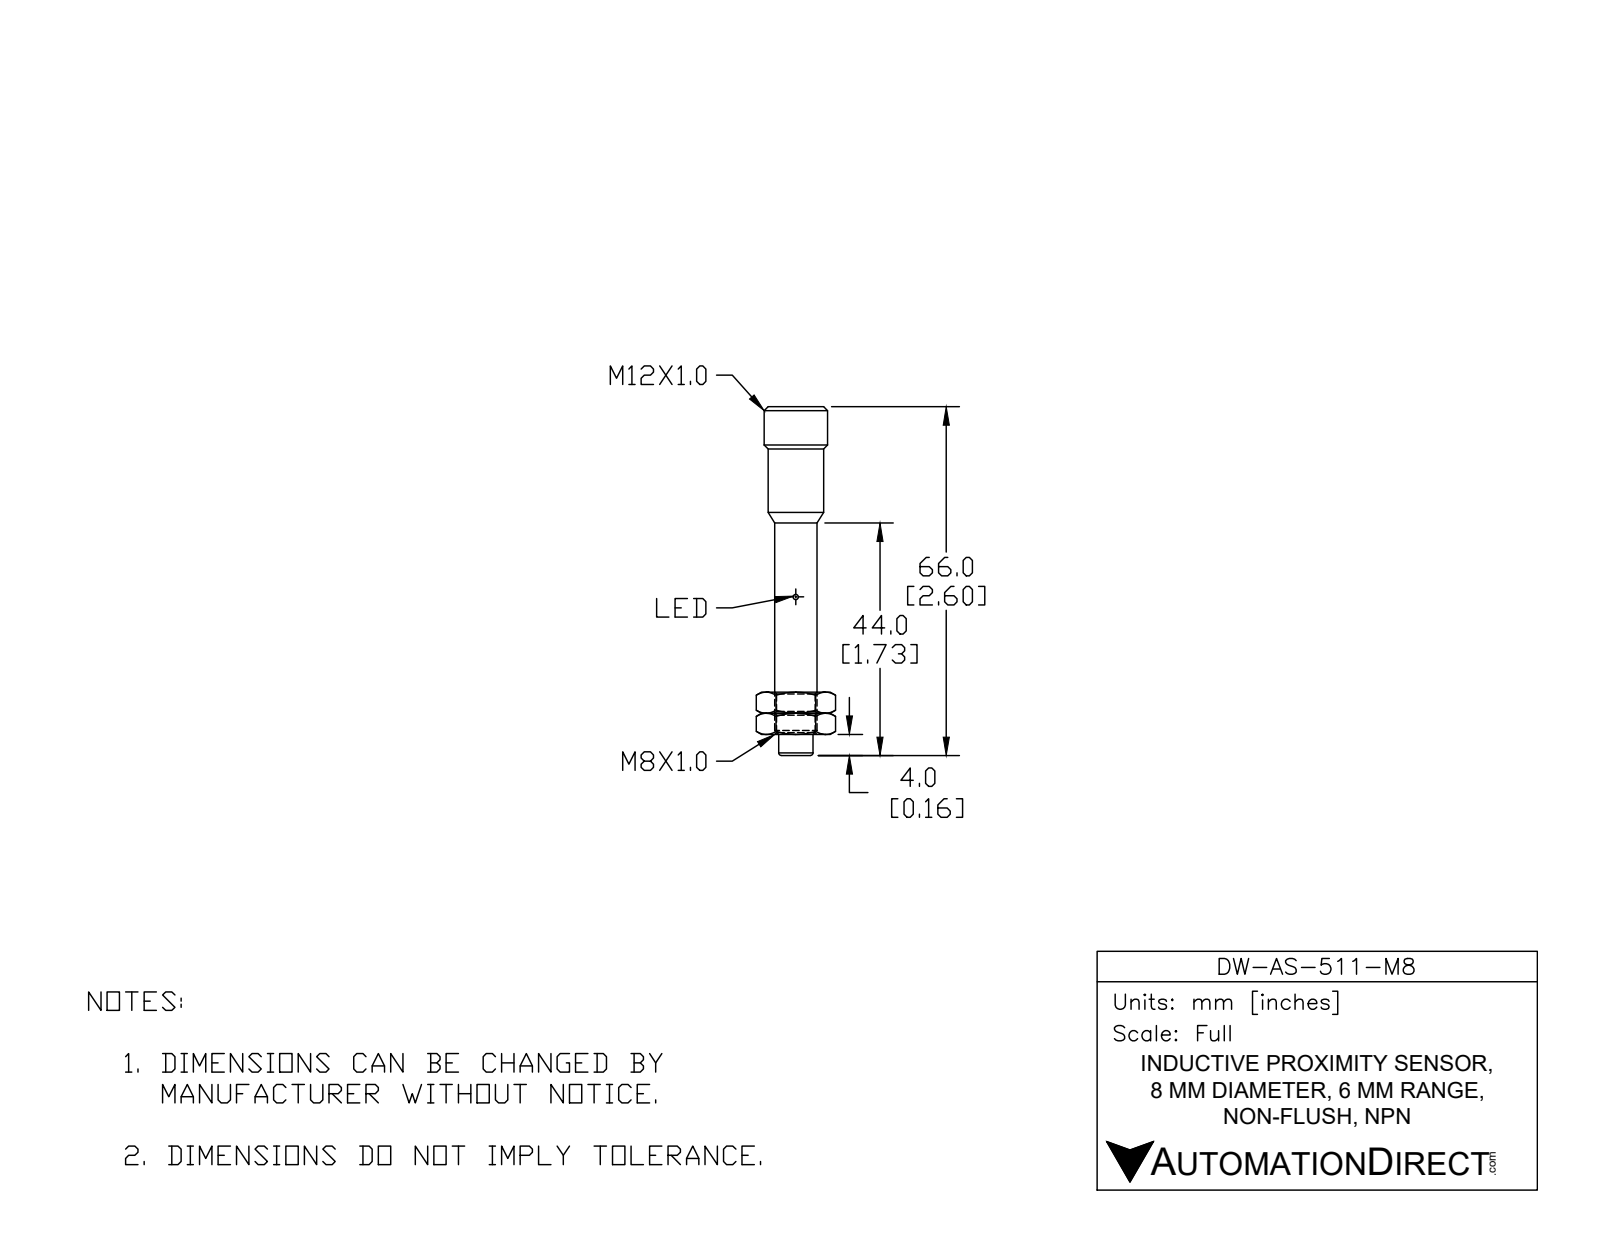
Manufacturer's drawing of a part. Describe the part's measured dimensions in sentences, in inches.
The part is named "DW-AS-511-M8". Its 3-D file was written by "SolidWorks 2017 (AUTOMOTIVE_DESIGN)". It is 1 solid with 35 faces: 10 planar, 17 cylindrical and 8 other. Overall it measures 2.599 by 0.472 by 0.472 inches. Its volume is 0.225 cubic inches and its surface area 3.685 square inches. Round holes: 2 of diameter 0.12. Round bosses or shafts: 4 of diameter 0.039, 1 of diameter 0.472, 1 of diameter 0.415, 1 of diameter 0.335, 1 of diameter 0.315, 1 of diameter 0.272. The main face-to-face distances are 0.343, 2.256, 2.598, 1.811, 0.445, 0.787, 0.165, 1.646, 2.091, 2.433.
